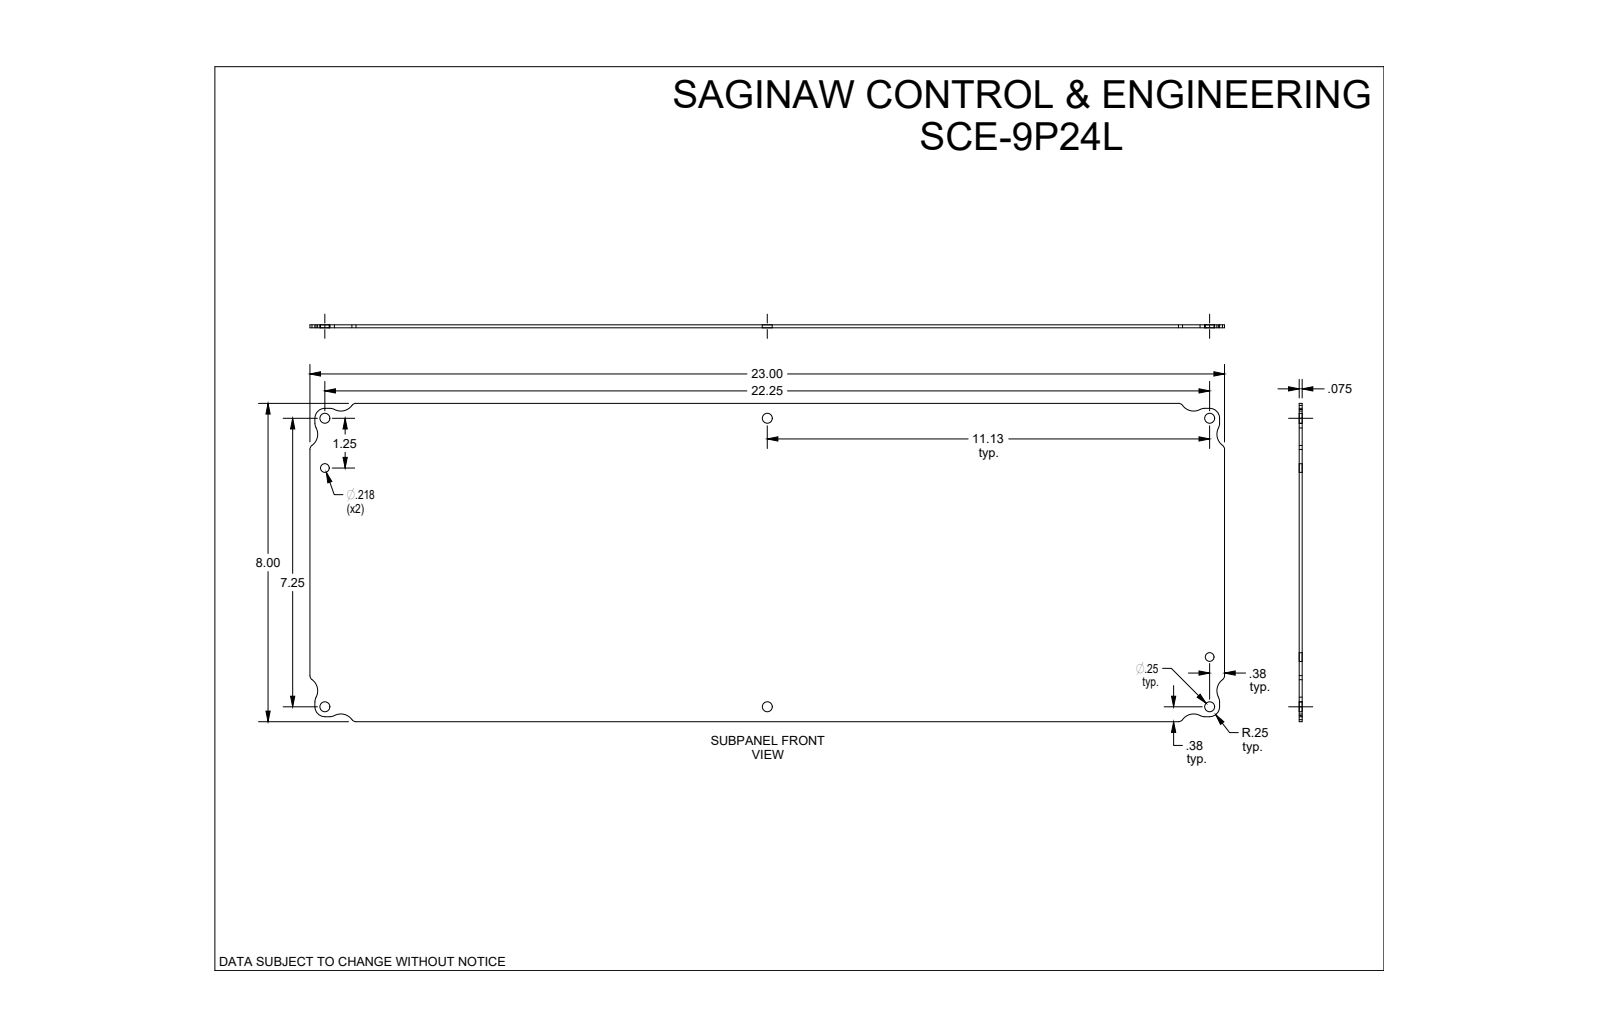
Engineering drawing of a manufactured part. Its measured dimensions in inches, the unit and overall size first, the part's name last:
Units: inches
Overall size (bounding box): 23 × 8 × 0.075
Round holes (diameter × count): ⌀0.25 ×6, ⌀0.218 ×2
Partial cylindrical surfaces — rounded edges, fillets, slot ends (radius × count): R0.25 ×12, R0.125 ×8, R0.344 ×8
Main face-to-face distances: 0.075, 8, 23, 0.125, 22.875, 0.125, 7.875, 22.75, 7.75
Hole centre spacings: 11.125, 13.278, 7.25, 1.25, 6, 11.195, 12.639, 22.25
Volume: 13.68 in³ · Surface area: 369.9 in²
Bodies: 1 solid, 50 faces (14 planar, 36 cylindrical, 0 other)
Part name (STEP PRODUCT): SCE-9P24L
STEP written by: SolidWorks 2019 (CONFIG_CONTROL_DESIGN)
